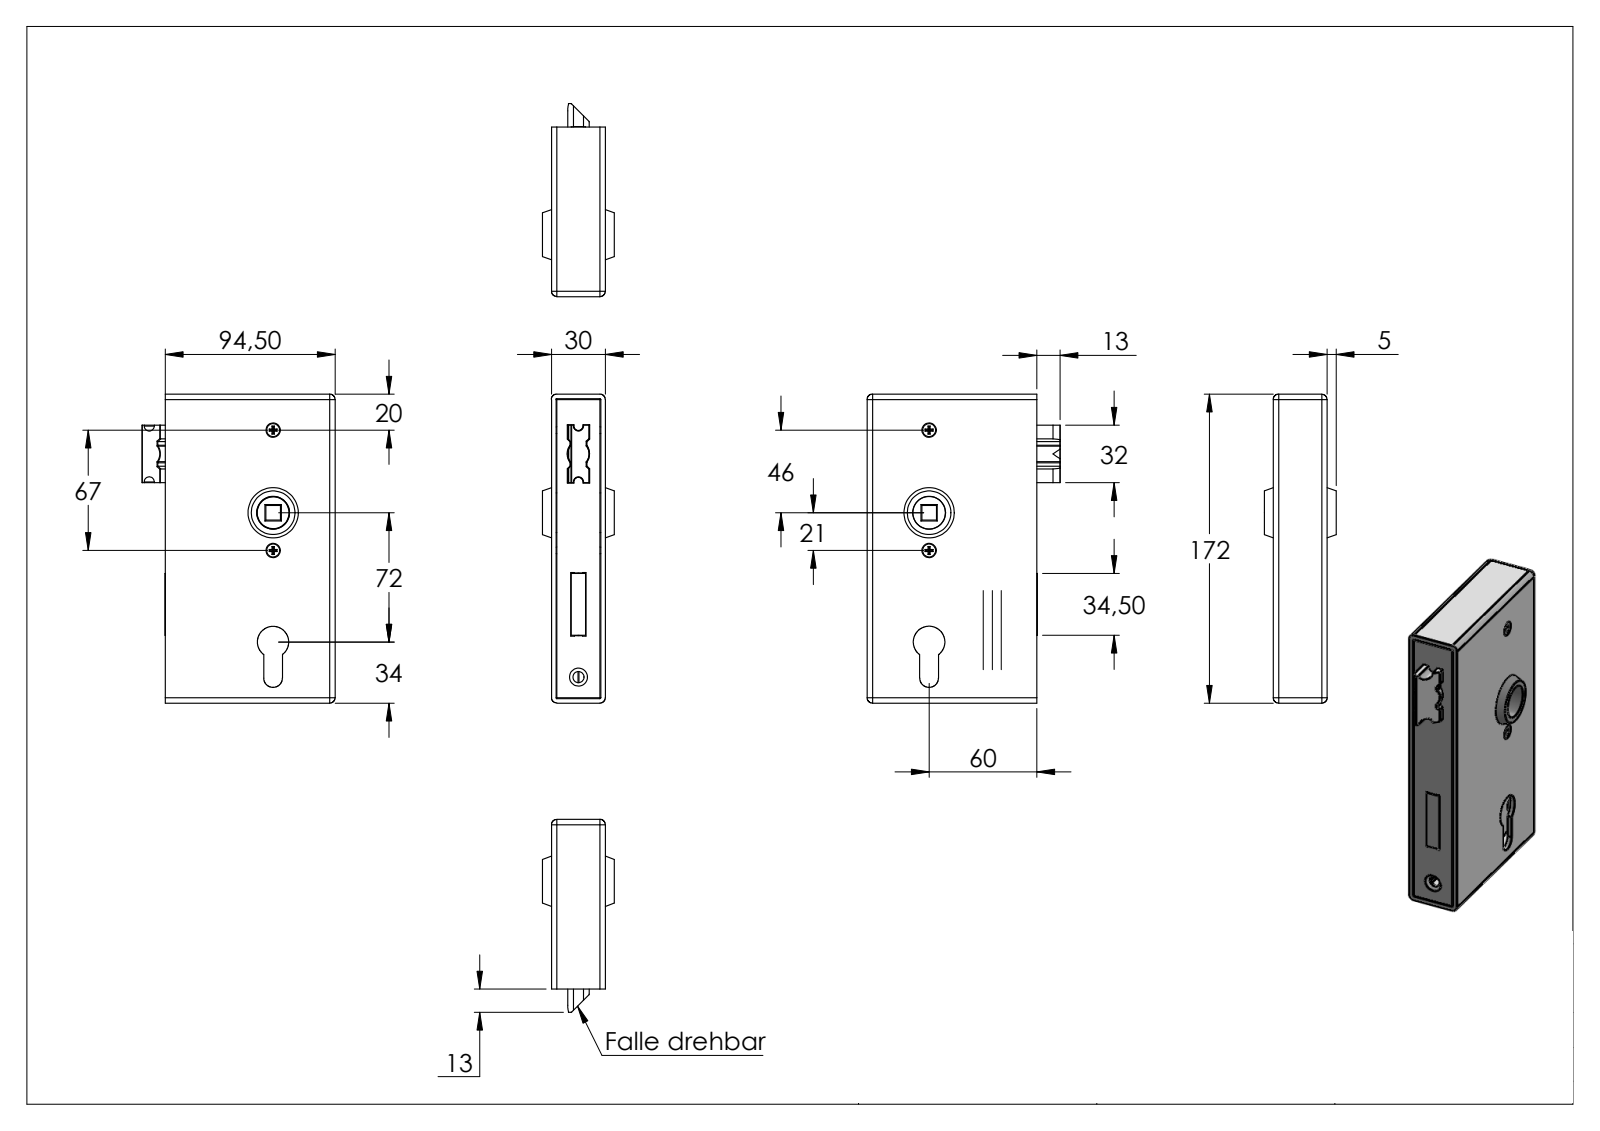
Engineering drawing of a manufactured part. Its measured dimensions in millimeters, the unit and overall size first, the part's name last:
Units: millimetres
Overall size (bounding box): 172 × 107.5 × 40
Round holes (diameter × count): ⌀8 ×6, ⌀3.3 ×2, ⌀4.6 ×2, ⌀6.2 ×1, ⌀8.2 ×1, ⌀17.5 ×1, ⌀18.3 ×1, ⌀22 ×1
Round bosses / shafts (diameter × count): ⌀7.2 ×2, ⌀4 ×2, ⌀3.6 ×2, ⌀18.1 ×1, ⌀8 ×1
Partial cylindrical surfaces — rounded edges, fillets, slot ends (radius × count): R0.5 ×13, R1 ×12, R3 ×8, R2 ×6, R0.1 ×4, R2.55 ×2, R2.8 ×2, R3.9 ×2
Main face-to-face distances: 2.5, 27.5, 8, 1, 5.5, 6.5, 9, 13, 18.5, 19.5
Hole centre spacings: 19, 20.62, 28.32, 38, 49.77, 61.98, 74.46, 80
Volume: 155 079 mm³ · Surface area: 157 247 mm²
Bodies: 13 solids, 712 faces (346 planar, 185 cylindrical, 181 other)
Part name (STEP PRODUCT): 564152+3 Teil3; DIN 965; 564152+3 Teil2; 564152+3 Teil3_564152+3 Teil3 (+5 more)
STEP written by: SolidWorks 2018 (CONFIG_CONTROL_DESIGN)
